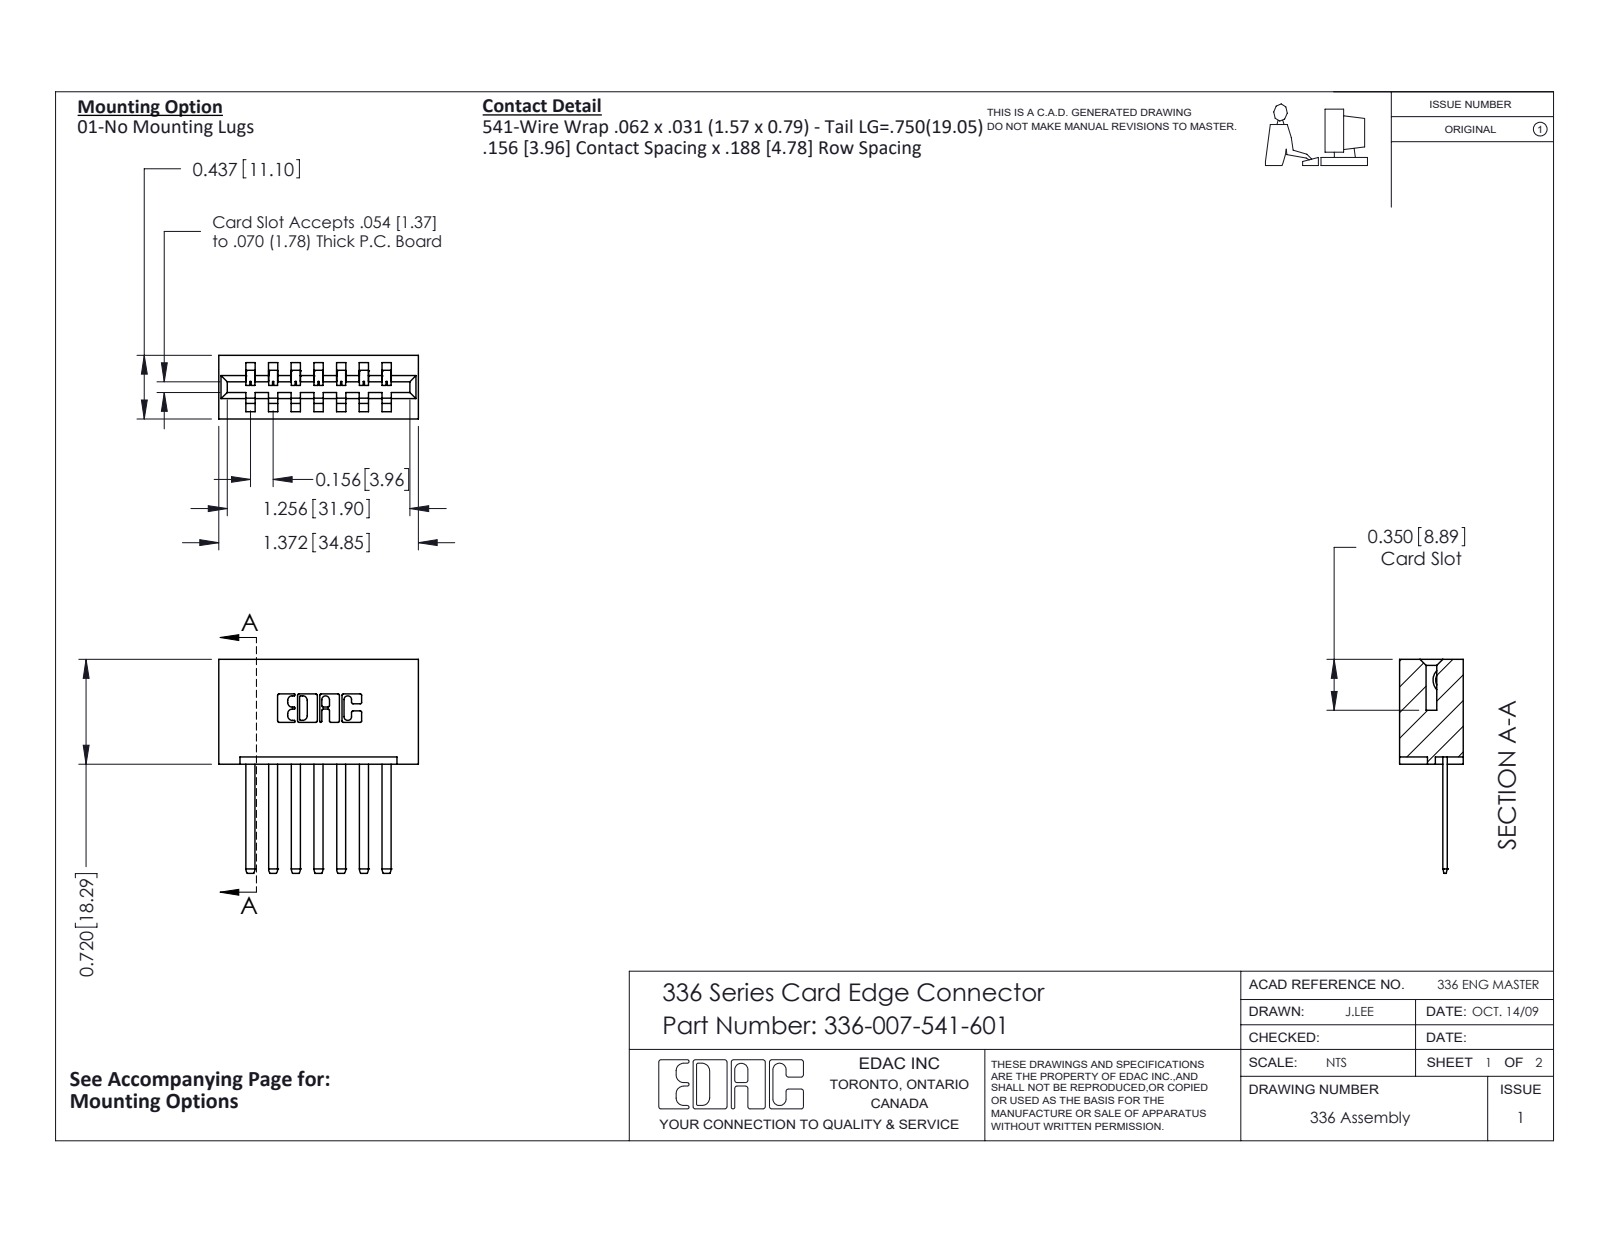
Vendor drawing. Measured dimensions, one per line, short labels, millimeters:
name: 336-007-541-601; 336 Part_Lugless; 336-290-001_336-290-541
written by: SolidWorks 2020 (CONFIG_CONTROL_DESIGN)
unit: mm
bodies: 8 solids, 456 faces (304 planar, 152 cylindrical, 0 other)
size: 37.3 × 34.8 × 11.1
volume: 5 600 mm³; area: 5 685 mm²
rounds: 22× R0.3, 14× R0.1, 14× R1.4, 6× R0.2, 6× R0.8, 3× R0.7, 2× R0.6, 2× R1
face distances: 4, 11.1, 7.9, 7.9, 5.6, 11.9, 15.8, 4.6, 1.3, 6.5
